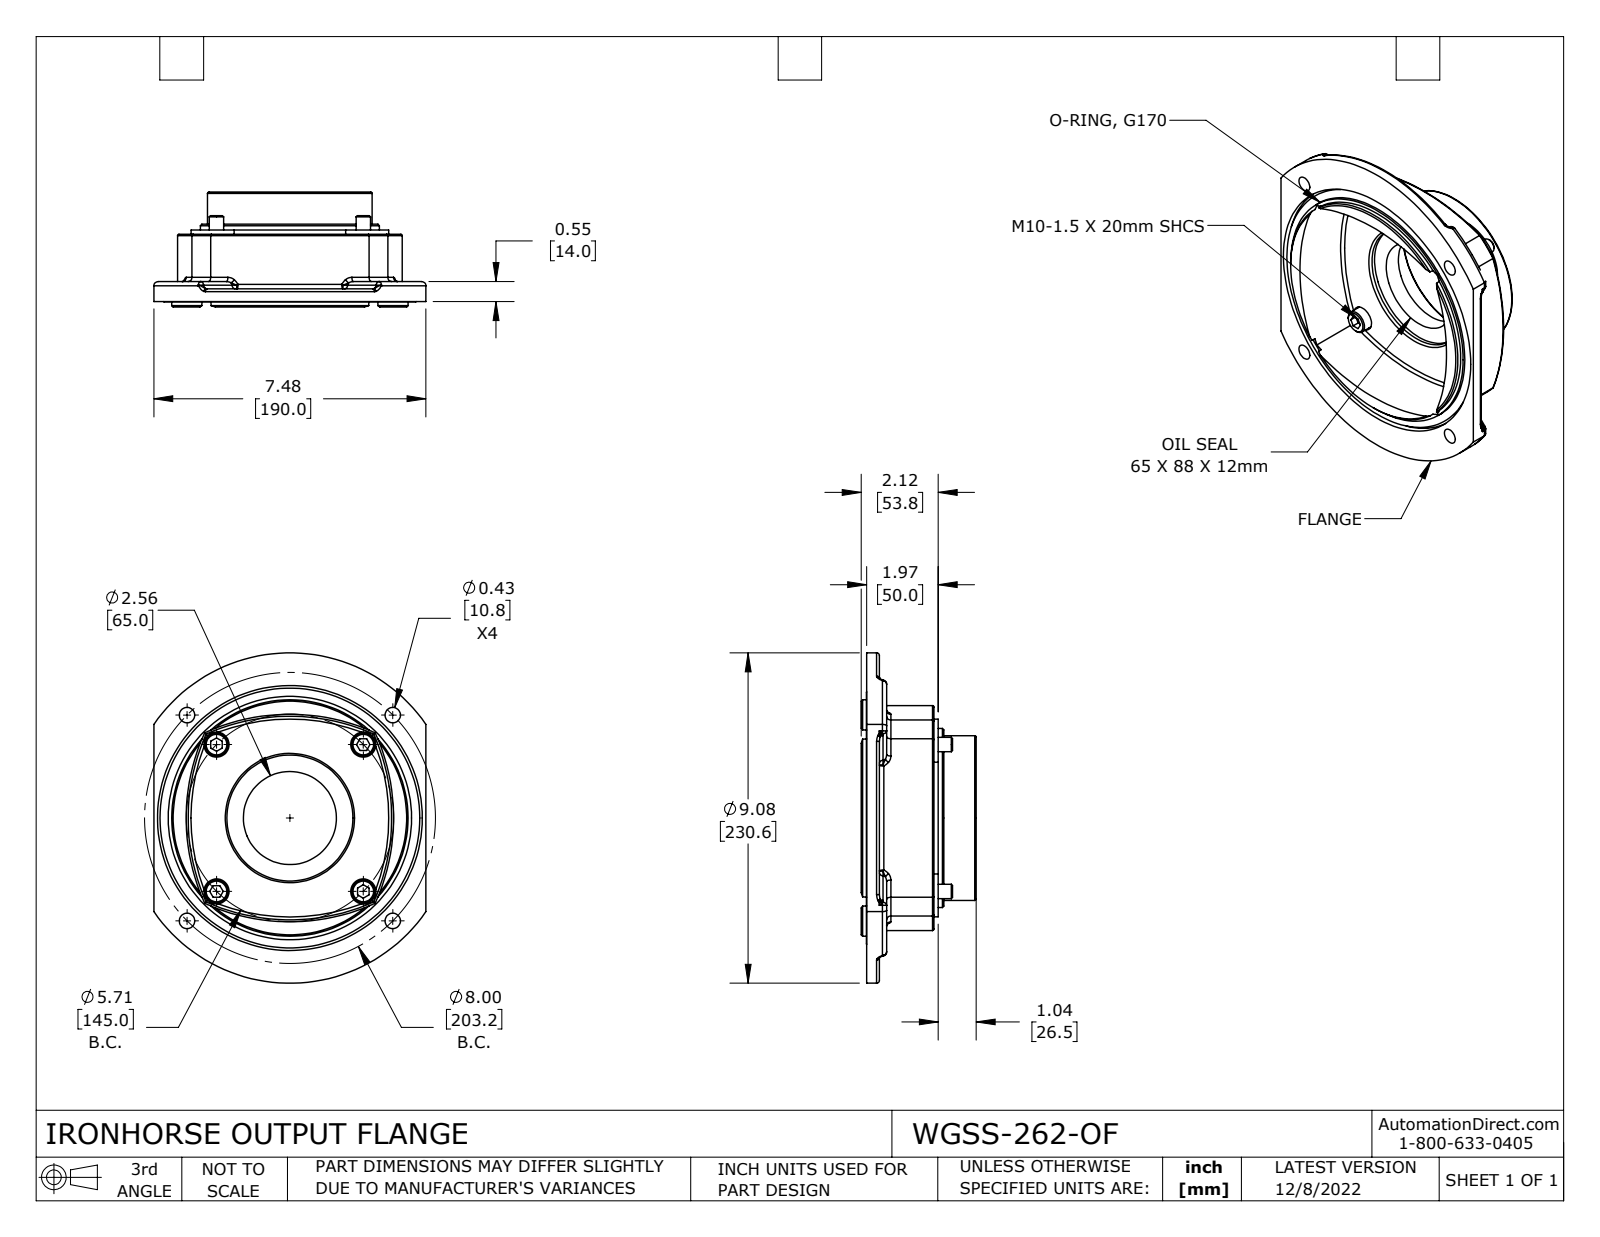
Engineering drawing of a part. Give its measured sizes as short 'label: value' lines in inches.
name: WGSS-262-OF
written by: SolidWorks 2021 (CONFIG_CONTROL_DESIGN)
unit: in
bodies: 7 solids, 360 faces (77 planar, 110 cylindrical, 173 other)
size: 9.08 × 7.48 × 3.163
volume: 37.65 in³; area: 267.4 in²
holes: 4× ⌀0.425, 4× ⌀0.433, 4× ⌀0.689, 1× ⌀2.559, 1× ⌀3.228, 1× ⌀3.268, 1× ⌀3.465, 1× ⌀3.583, 1× ⌀3.937, 1× ⌀7.283
bosses: 4× ⌀0.63, 4× ⌀0.394, 1× ⌀6.693, 1× ⌀6.5, 1× ⌀4.921, 1× ⌀4.528, 1× ⌀2.795
rounds: 14× R0.118, 4× R1.181, 4× R6.181, 2× R0.079, 1× R3.465, 1× R4.54
face distances: 0.354, 1.458, 1.104, 0.512, 0.217, 1.615, 1.97, 0.551, 0.118, 0.394
hole spacings: 4.914, 1.145, 2.855, 4, 4.037, 5.657, 6.854, 5.709
